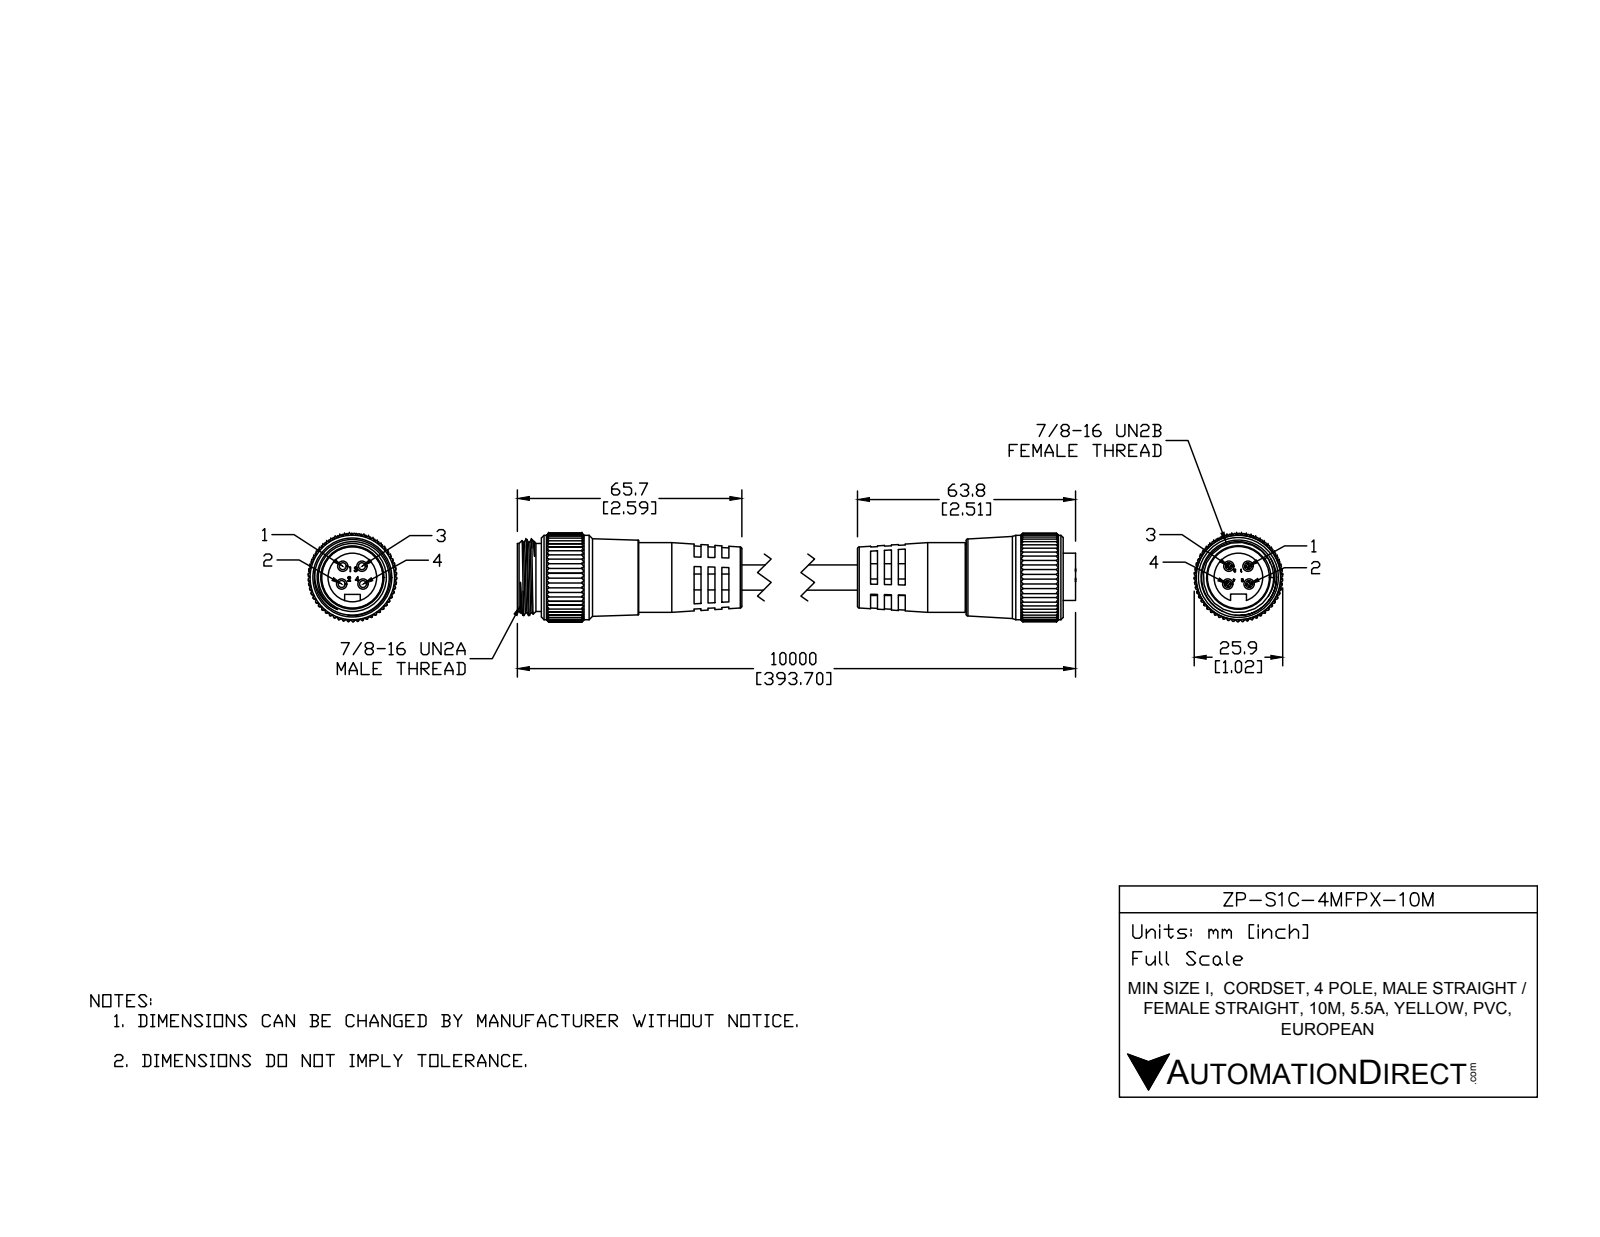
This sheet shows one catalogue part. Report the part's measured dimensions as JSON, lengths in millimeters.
{"part_name": "ZP-S1C-4MFPX-10M", "step_written_by": "SolidWorks 2015 (AUTOMOTIVE_DESIGN)", "units": "millimeters", "bodies": {"solids": 8, "faces": 1161, "planar": 427, "cylindrical": 634, "other": 100}, "overall_size": [229.66, 25.84, 25.83], "volume_mm3": 51474, "surface_area_mm2": 24731, "round_holes": [[3.05, 4], [19.96, 1], [20.45, 1], [21, 1]], "round_bosses_or_shafts": [[3.05, 4], [2, 4], [24.68, 1], [22.22, 1], [20.4, 1], [19.5, 1], [17.88, 1], [14.22, 1]], "partial_cylinders_radius": [[0.25, 165], [2.29, 1], [5.25, 1], [12.93, 1]], "face_to_face_distances": [2, 4.02, 117.68, 113.65, 4.03, 125.74, 59.84, 4.04, 121.7, 121.72], "hole_center_spacings": [3.67, 5.24, 4.32, 4.33, 5.59, 6.24, 7.89, 7.9]}
